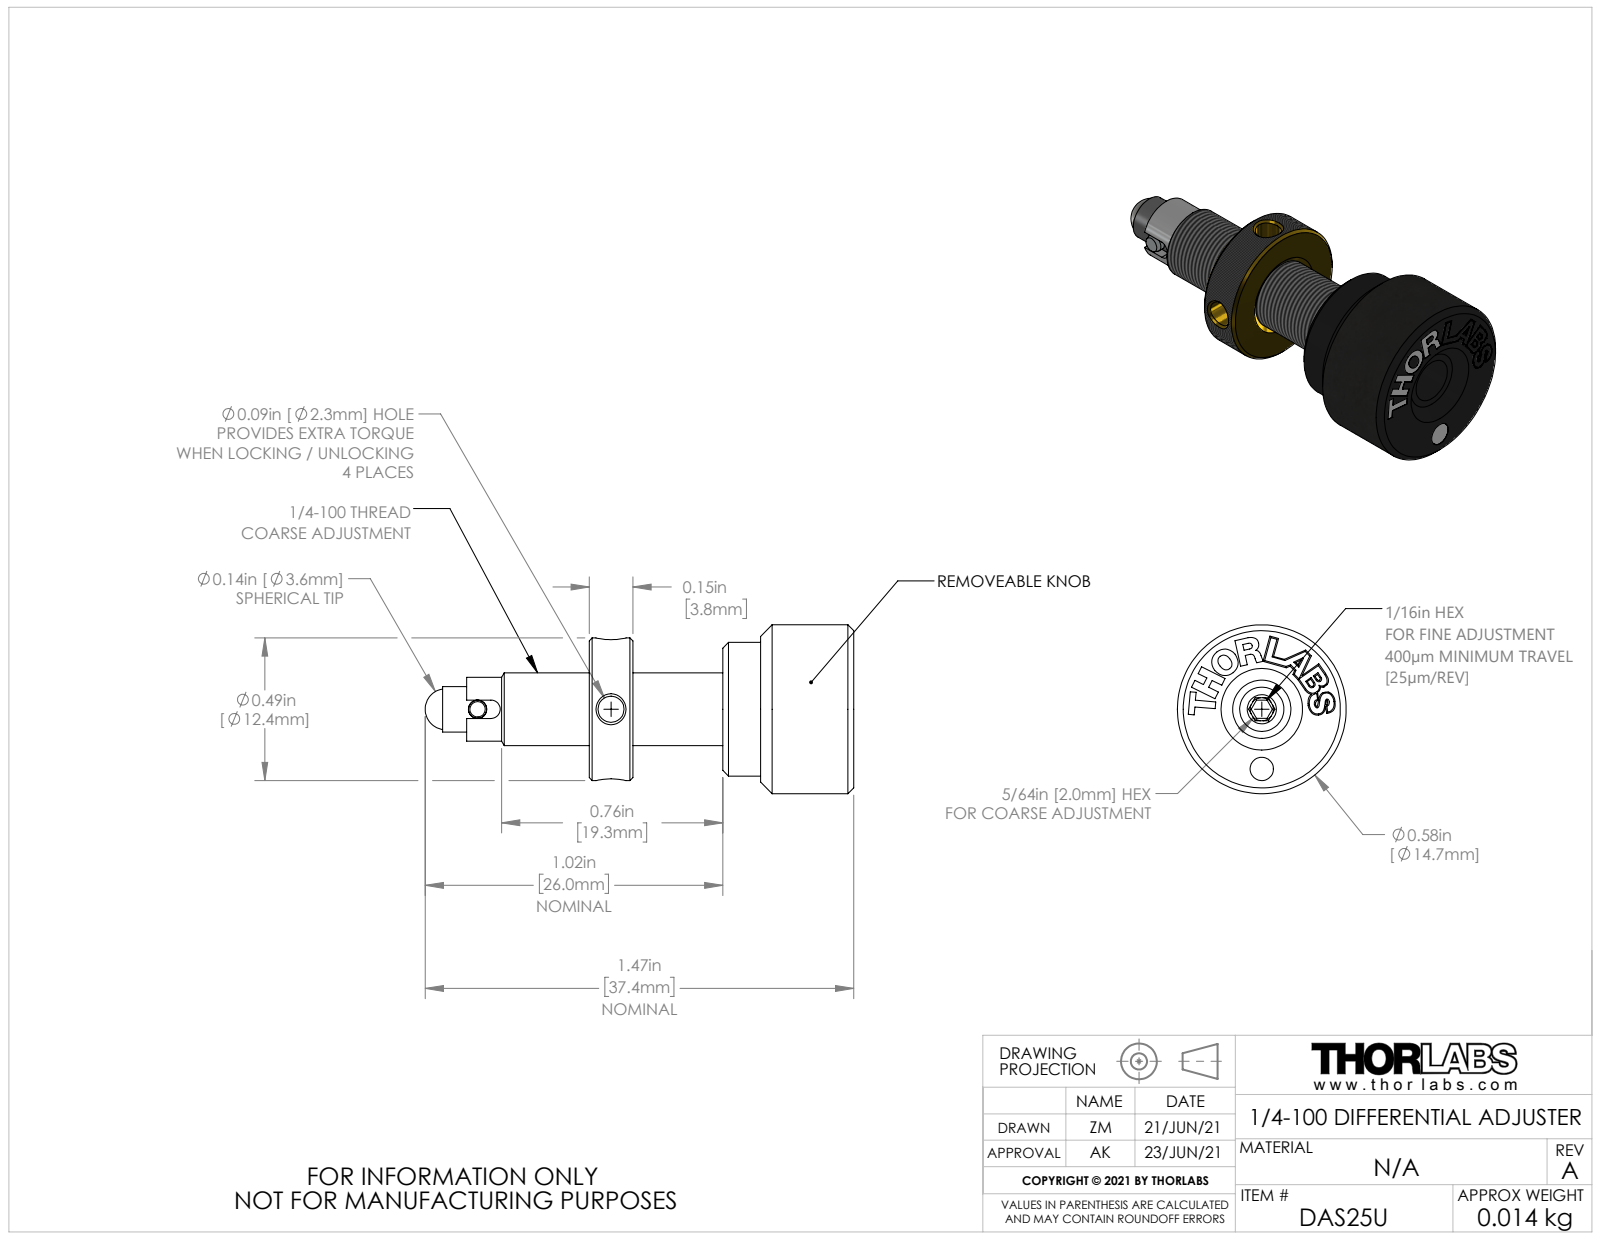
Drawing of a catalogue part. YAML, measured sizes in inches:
part_name: "TTN253563-E0W"
step_written_by: "SolidWorks 2018 (AUTOMOTIVE_DESIGN)"
units: inches
bodies: {solids: 8, faces: 343, planar: 160, cylindrical: 72, other: 111}
overall_size: [1.473, 0.58, 0.58]
volume: 0.151
surface_area: 4.693
round_holes:
  - {diameter: 0.09, count: 2}
  - {diameter: 0.063, count: 1}
  - {diameter: 0.07, count: 1}
  - {diameter: 0.08, count: 1}
  - {diameter: 0.098, count: 1}
  - {diameter: 0.118, count: 1}
  - {diameter: 0.141, count: 1}
  - {diameter: 0.152, count: 1}
  - {diameter: 0.157, count: 1}
  - {diameter: 0.183, count: 1}
  - {diameter: 0.21, count: 1}
  - {diameter: 0.245, count: 1}
round_bosses_or_shafts:
  - {diameter: 0.58, count: 1}
  - {diameter: 0.49, count: 1}
  - {diameter: 0.46, count: 1}
  - {diameter: 0.22, count: 1}
  - {diameter: 0.209, count: 1}
  - {diameter: 0.197, count: 1}
  - {diameter: 0.157, count: 1}
  - {diameter: 0.156, count: 1}
partial_cylinders:
  - {radius: 0.014, count: 1}
  - {radius: 0.032, count: 1}
  - {radius: 0.047, count: 1}
  - {radius: 0.059, count: 1}
face_to_face_distances: [0.15, 0.909, 0.759, 0.27, 0.639, 0.489, 0.459, 0.309, 0.18, 0.45]
hole_center_spacings: [0.205, 0.459]
